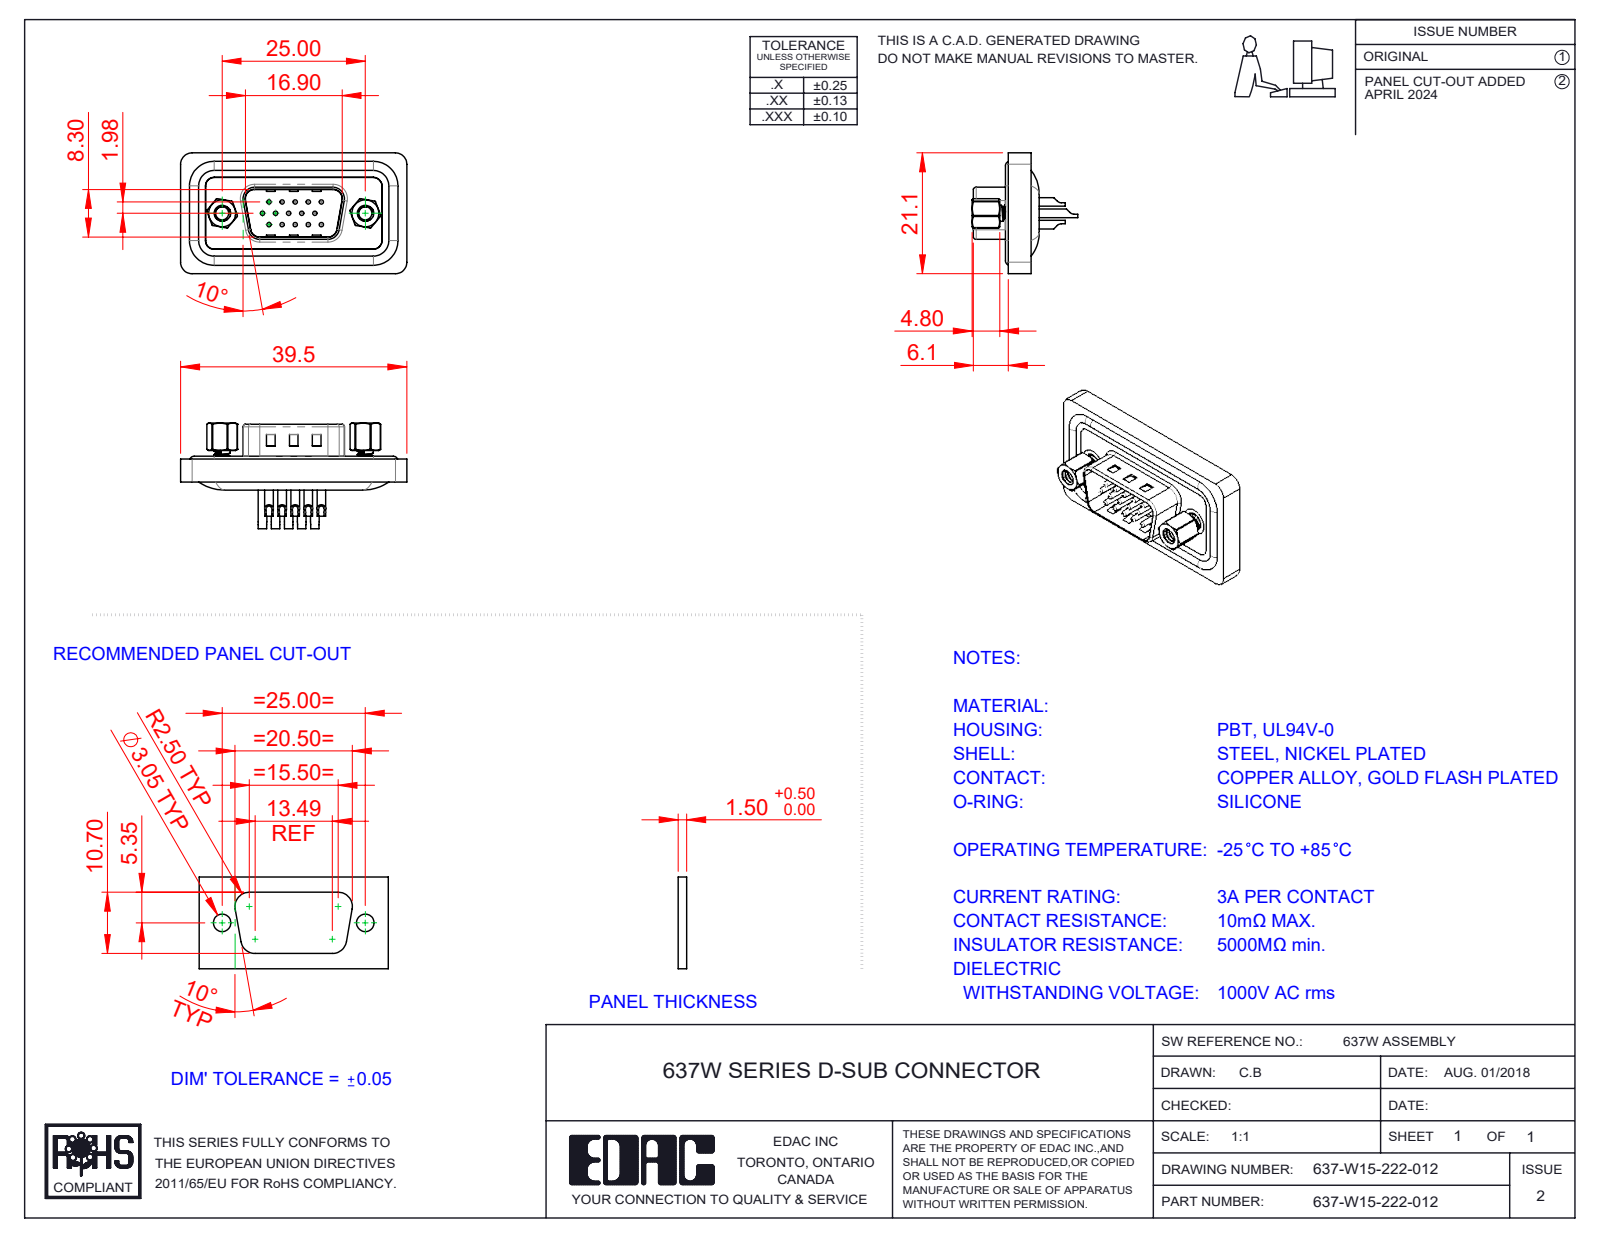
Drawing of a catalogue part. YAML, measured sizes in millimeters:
part_name: "637W Contact Row 3_22; 637W 4-40 Hex Standoff; 637W Shell_15 Contacts; 637W Housing_15 Contacts (+5 more)"
step_written_by: "SolidWorks 2023 (CONFIG_CONTROL_DESIGN)"
units: millimeters
bodies: {solids: 23, faces: 1033, planar: 276, cylindrical: 482, other: 275}
overall_size: [39.51, 21.1, 18.45]
volume: 4037
surface_area: 6988
round_holes:
  - {diameter: 0.75, count: 15}
  - {diameter: 1, count: 15}
  - {diameter: 1.5, count: 15}
  - {diameter: 1.6, count: 15}
  - {diameter: 2, count: 15}
  - {diameter: 2.26, count: 2}
  - {diameter: 2.29, count: 2}
  - {diameter: 4, count: 2}
  - {diameter: 4.8, count: 2}
  - {diameter: 5, count: 2}
round_bosses_or_shafts:
  - {diameter: 1.5, count: 8}
  - {diameter: 1.6, count: 4}
  - {diameter: 4.9, count: 2}
  - {diameter: 2.79, count: 2}
  - {diameter: 5, count: 1}
partial_cylinders:
  - {radius: 1.5, count: 14}
  - {radius: 2, count: 14}
  - {radius: 0.5, count: 8}
  - {radius: 2.7, count: 6}
  - {radius: 0.9, count: 4}
  - {radius: 1.6, count: 4}
  - {radius: 4.3, count: 4}
  - {radius: 1, count: 3}
face_to_face_distances: [0.4, 1.6, 1.1, 2.9, 2.5, 0.5, 4, 3.6, 0.7, 3.4]
hole_center_spacings: [3.96, 2.28, 4.57, 2.29, 6.05, 6.04, 7.92, 6.86]
